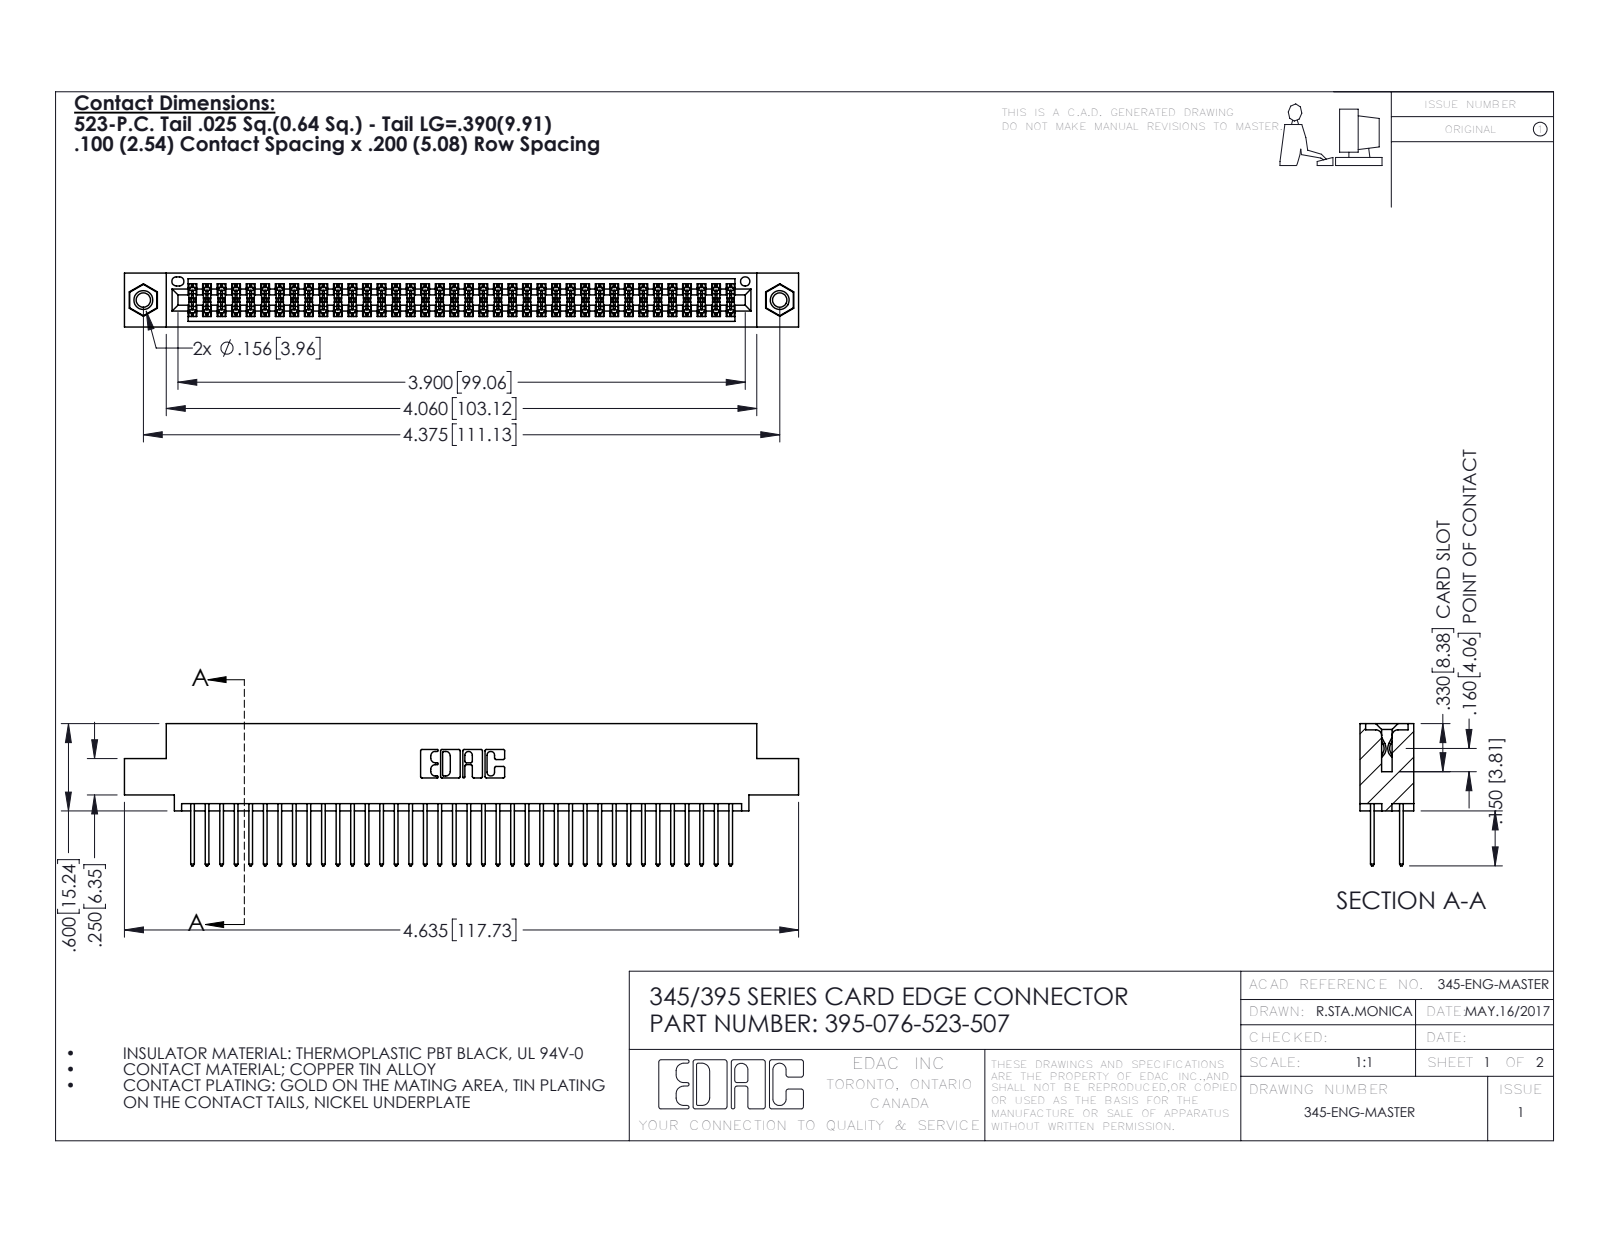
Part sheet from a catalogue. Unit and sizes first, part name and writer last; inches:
Units: inches
Overall size (bounding box): 4.635 × 0.977 × 0.37
Round holes (diameter × count): ⌀0.098 ×2, ⌀0.125 ×2, ⌀0.156 ×2, ⌀0.064 ×1
Round bosses / shafts (diameter × count): ⌀0.155 ×2
Partial cylindrical surfaces — rounded edges, fillets, slot ends (radius × count): R0.006 ×114, R0.01 ×76, R0.01 ×22, R0.007 ×6, R0.031 ×6, R0.026 ×3, R0.014 ×2, R0.019 ×2
Main face-to-face distances: 0.072, 0.298, 0.2, 0.098, 0.272, 0.025, 0.37, 0.225, 0.175, 0.149
Hole centre spacings: 0.27, 4.139, 4.375
Volume: 0.7 in³ · Surface area: 27.43 in²
Bodies: 79 solids, 3990 faces (2624 planar, 1350 cylindrical, 16 other)
Part name (STEP PRODUCT): 345-292-001_345-293-123; 395-076-523-507; 345 Part_0.110 Offset - 0.156 Dia-TI; 345-250-001_345-250-005-103
STEP written by: SolidWorks 2016 (CONFIG_CONTROL_DESIGN)
